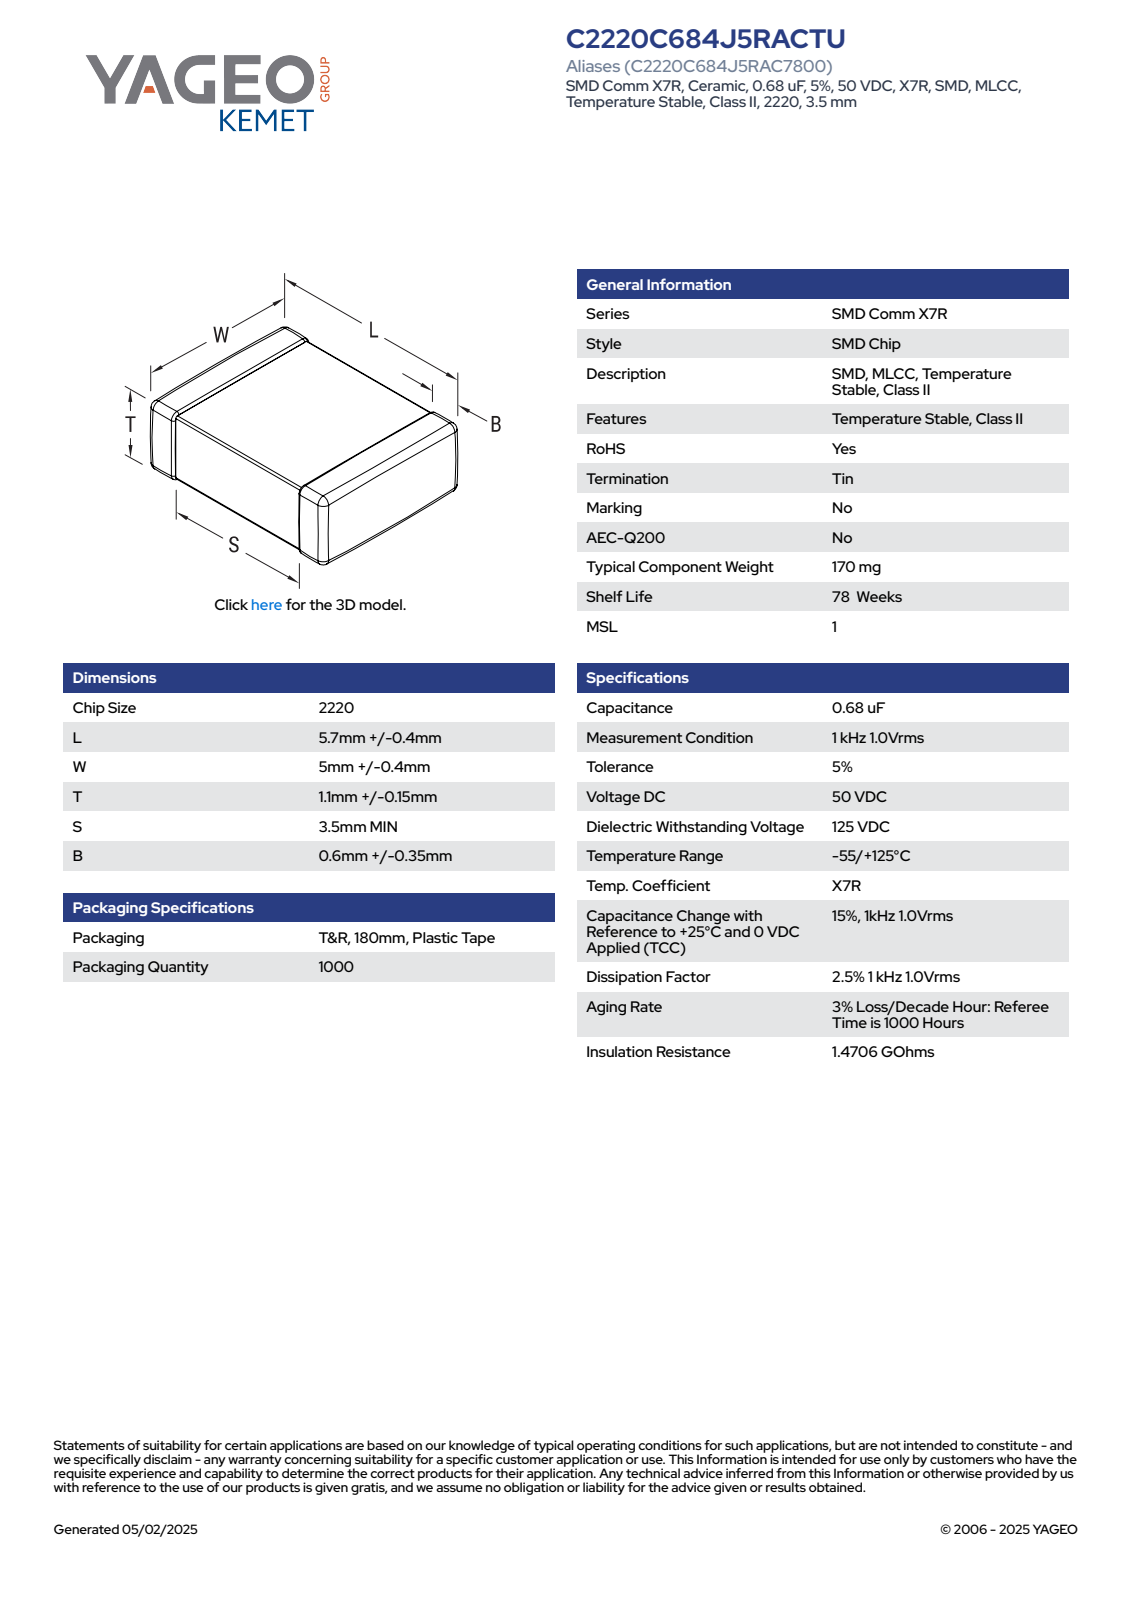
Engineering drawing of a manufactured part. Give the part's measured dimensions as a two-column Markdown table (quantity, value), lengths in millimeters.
| quantity | value |
| --- | --- |
| part name | CCS_CCSTD_2220_L6.1W5.4T1.25B0.6 |
| STEP written by | SolidWorks 2021 (AUTOMOTIVE_DESIGN) |
| units | millimeters |
| bodies | 4 solids, 125 faces (71 planar, 38 cylindrical, 16 other) |
| overall size | 6.1 × 5.4 × 1.25 |
| volume | 35 mm³ |
| surface area | 94 mm² |
| partial cylindrical surfaces (radius × count) | 0.11 × 24 |
| main face-to-face distances | 1.03, 1.14, 1.25, 6.1, 5.18, 5.29, 5.4, 2.5, 3.6, 3.29 |
